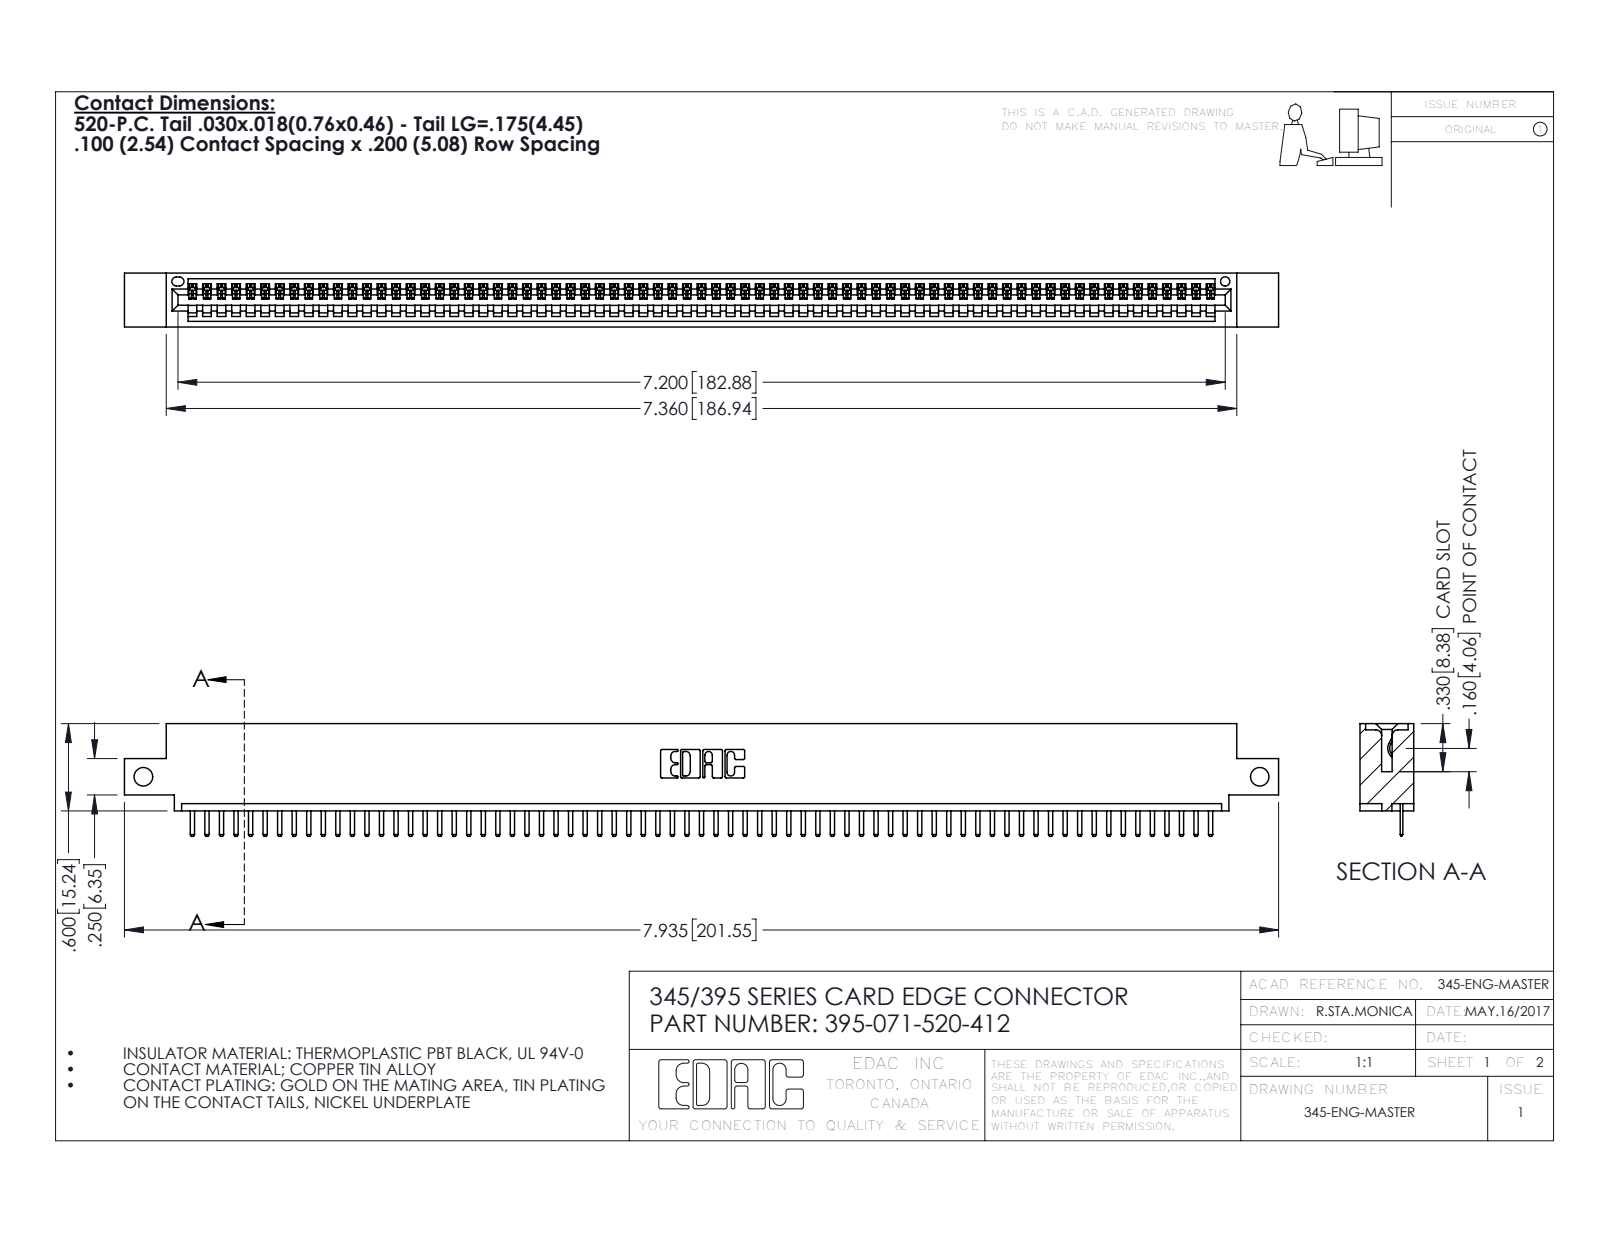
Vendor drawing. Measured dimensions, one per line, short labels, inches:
name: 345 Part_0.110 Offset - Side Mount; 345-292-001_345-293-120; 395-071-520-412
written by: SolidWorks 2016 (CONFIG_CONTROL_DESIGN)
unit: in
bodies: 72 solids, 4532 faces (3066 planar, 1466 cylindrical, 0 other)
size: 7.935 × 0.775 × 0.37
volume: 1.16 in³; area: 38.65 in²
holes: 2× ⌀0.128, 1× ⌀0.064
rounds: 144× R0.01, 142× R0.006, 22× R0.01, 6× R0.007, 6× R0.031, 3× R0.026, 2× R0.031, 2× R0.04
face distances: 0.298, 0.072, 0.37, 0.2, 0.098, 0.272, 0.025, 0.225, 0.072, 0.149
hole spacings: 7.675
